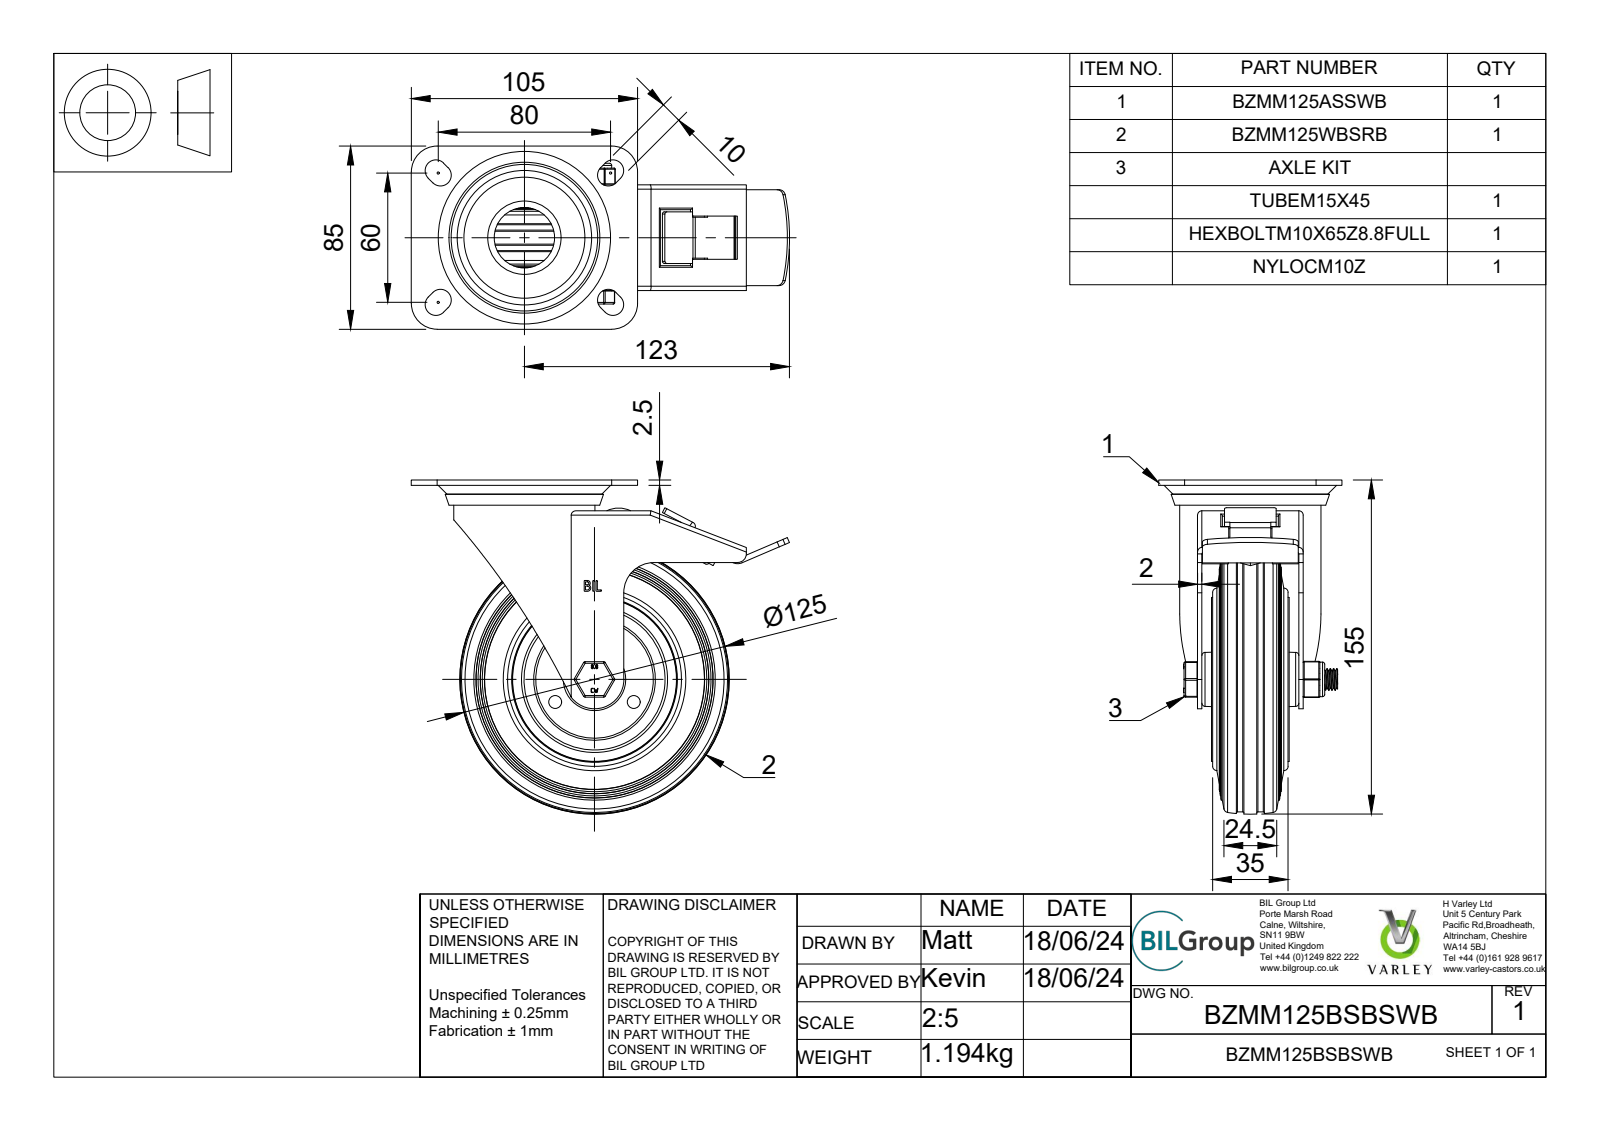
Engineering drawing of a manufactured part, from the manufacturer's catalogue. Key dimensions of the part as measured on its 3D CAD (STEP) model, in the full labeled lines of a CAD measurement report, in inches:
Part name (STEP PRODUCT): BZMM125BSBSWB v4; BZMM125ASSWB v1; ZINC PLATED, PRESSED STEEL TOP PLATE; ZINC PLATED, PRESSED STEEL FORKS (+8 more)
STEP written by: Autodesk Translation Framework v13.14.0.145 (AUTOMOTIVE_DESIGN)
Units: inches
Bodies: 26 solids, 847 faces (400 planar, 286 cylindrical, 161 other)
Overall size (bounding box): 6.909 × 6.102 × 3.346
Volume: 23.46 in³ · Surface area: 247.8 in²
Round holes (diameter × count): ⌀0.157 ×3, ⌀0.236 ×2, ⌀0.394 ×1, ⌀0.402 ×1, ⌀0.472 ×1, ⌀0.591 ×1, ⌀0.908 ×1, ⌀1.102 ×1, ⌀1.575 ×1, ⌀2.297 ×1, ⌀2.421 ×1, ⌀3.007 ×1
Round bosses / shafts (diameter × count): ⌀0.157 ×8, ⌀0.236 ×3, ⌀4.838 ×1, ⌀2.579 ×1, ⌀1.339 ×1, ⌀0.896 ×1, ⌀0.63 ×1, ⌀0.589 ×1
Partial cylindrical surfaces — rounded edges, fillets, slot ends (radius × count): R0.02 ×18, R0.03 ×16, R0.059 ×12, R0.197 ×9, R0.039 ×8, R0.079 ×6, R0.118 ×4, R0.472 ×4
Main face-to-face distances: 0.079, 0.197, 1.85, 0.098, 0.276, 0.118, 0.157, 0.906, 0.827, 0.354
Hole centre spacings: 0.828, 1.434, 0.828, 1.435, 1.722
